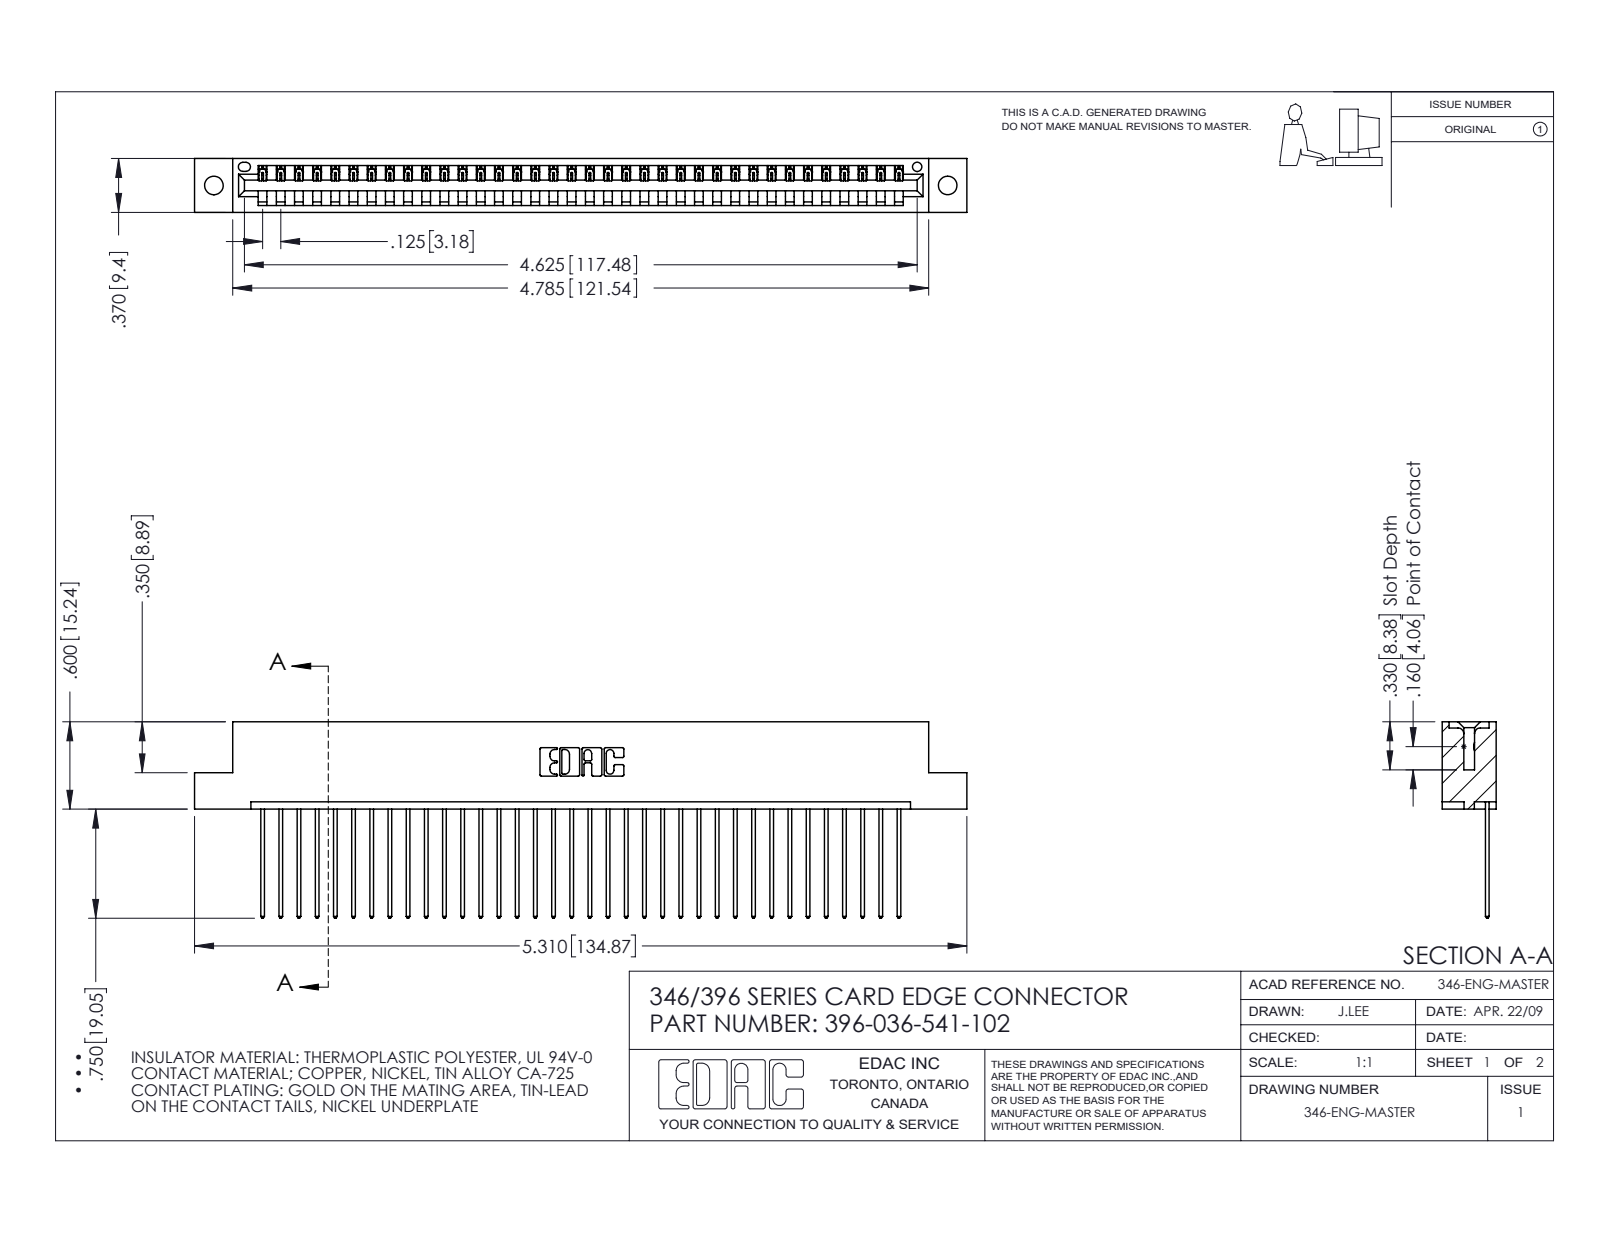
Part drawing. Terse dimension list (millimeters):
name: 396-036-541-102; 346 Part_Flush Mounting Lugs - 0.128 Dia; 345-292-001_345-293-141
written by: SolidWorks 2016 (CONFIG_CONTROL_DESIGN)
unit: mm
bodies: 37 solids, 2210 faces (1516 planar, 694 cylindrical, 0 other)
size: 134.9 × 34.3 × 9.4
volume: 12 900 mm³; area: 16 560 mm²
holes: 2× ⌀3.3, 1× ⌀1.6
rounds: 72× R0.2, 72× R0.3, 22× R0.3, 6× R0.2, 6× R0.8, 3× R0.7, 2× R0.8, 2× R1
face distances: 1.2, 8.2, 9.4, 6.4, 1.8, 7.6, 0.6, 3.8, 5.6, 2.5
hole spacings: 6.2, 122.8, 128.1
